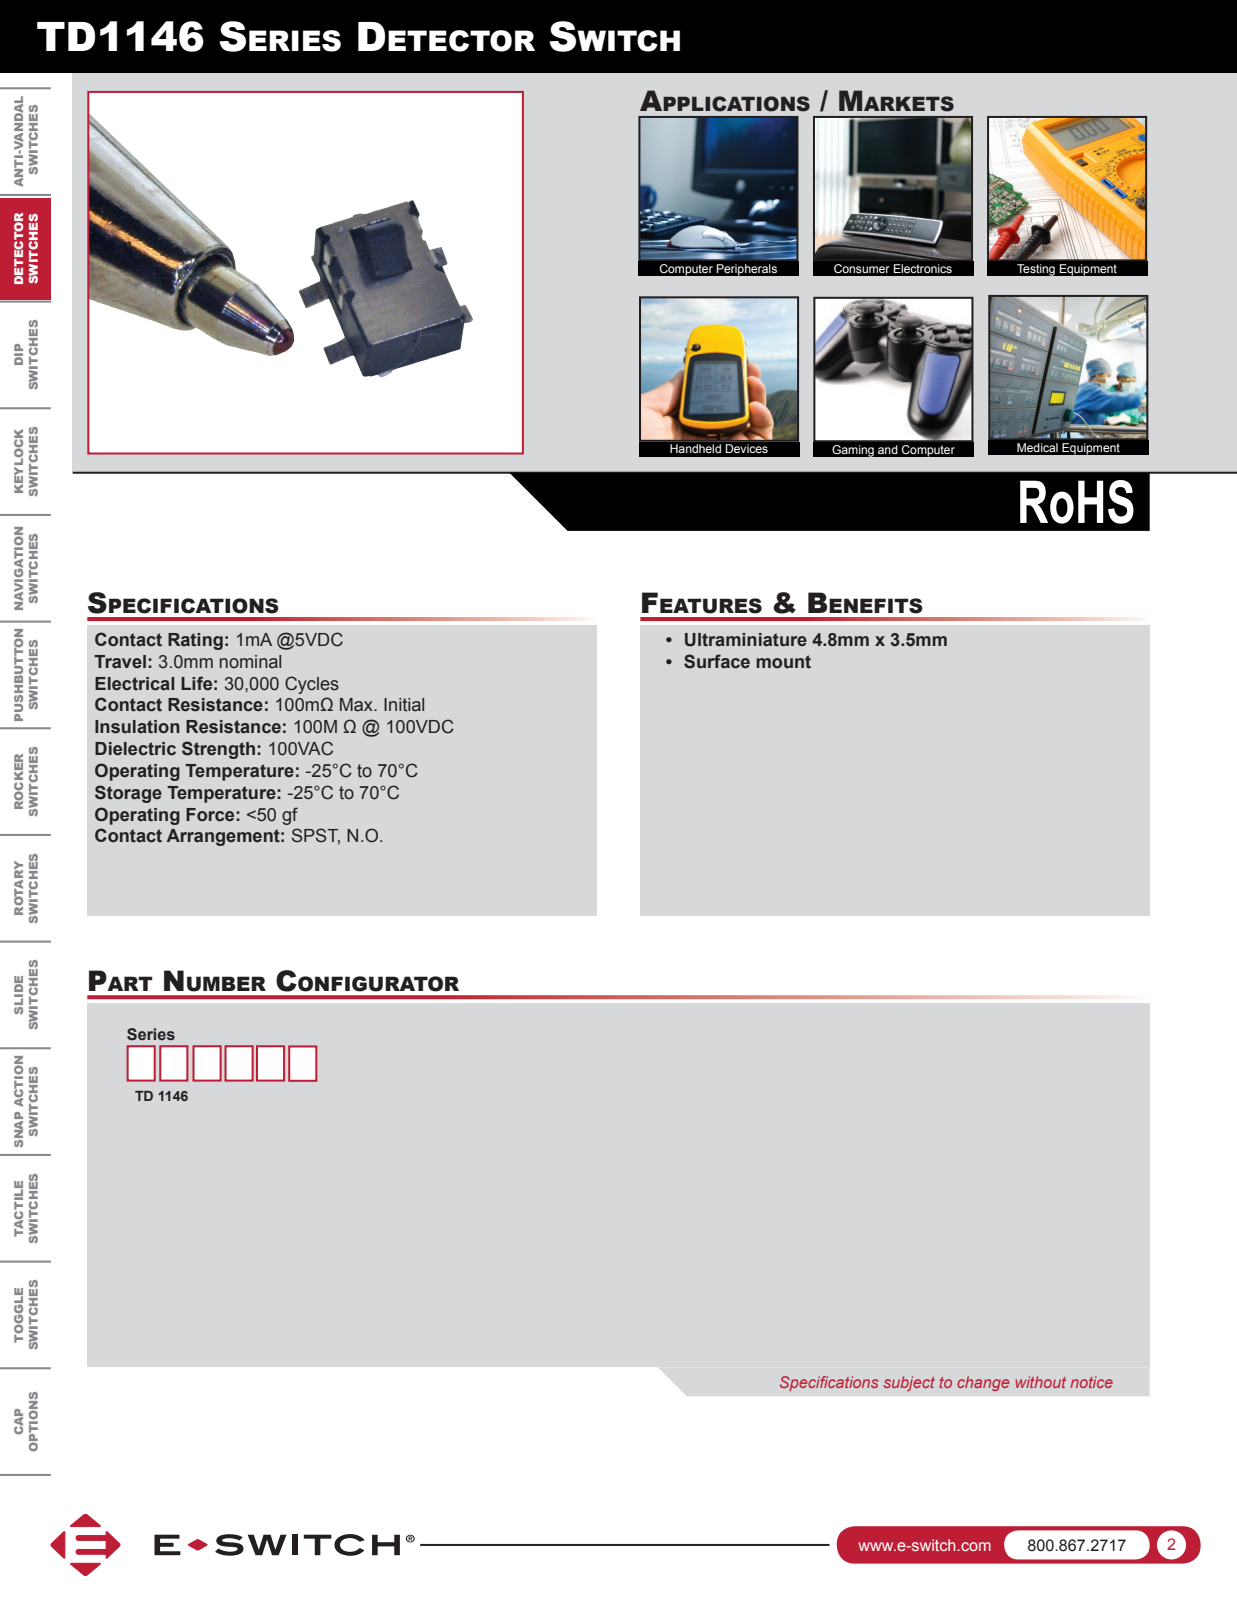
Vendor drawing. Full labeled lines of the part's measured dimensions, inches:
Part name (STEP PRODUCT): P:\\E-Switch Secure\\3D_MODELS_STP_FORMAT\\TD1146.stp
STEP written by: ACIS (CONFIG_CONTROL_DESIGN)
Units: inches
Bodies: 1 solid, 126 faces (113 planar, 13 cylindrical, 0 other)
Overall size (bounding box): 0.197 × 0.189 × 0.148
Volume: 0.002 in³ · Surface area: 0.167 in²
Round bosses / shafts (diameter × count): ⌀0.014 ×1
Partial cylindrical surfaces — rounded edges, fillets, slot ends (radius × count): R0.008 ×5, R0.012 ×4, R0.004 ×2, R0.118 ×1
Main face-to-face distances: 0.091, 0.041, 0.094, 0.189, 0.138, 0.039, 0.051, 0.043, 0.053, 0.096
